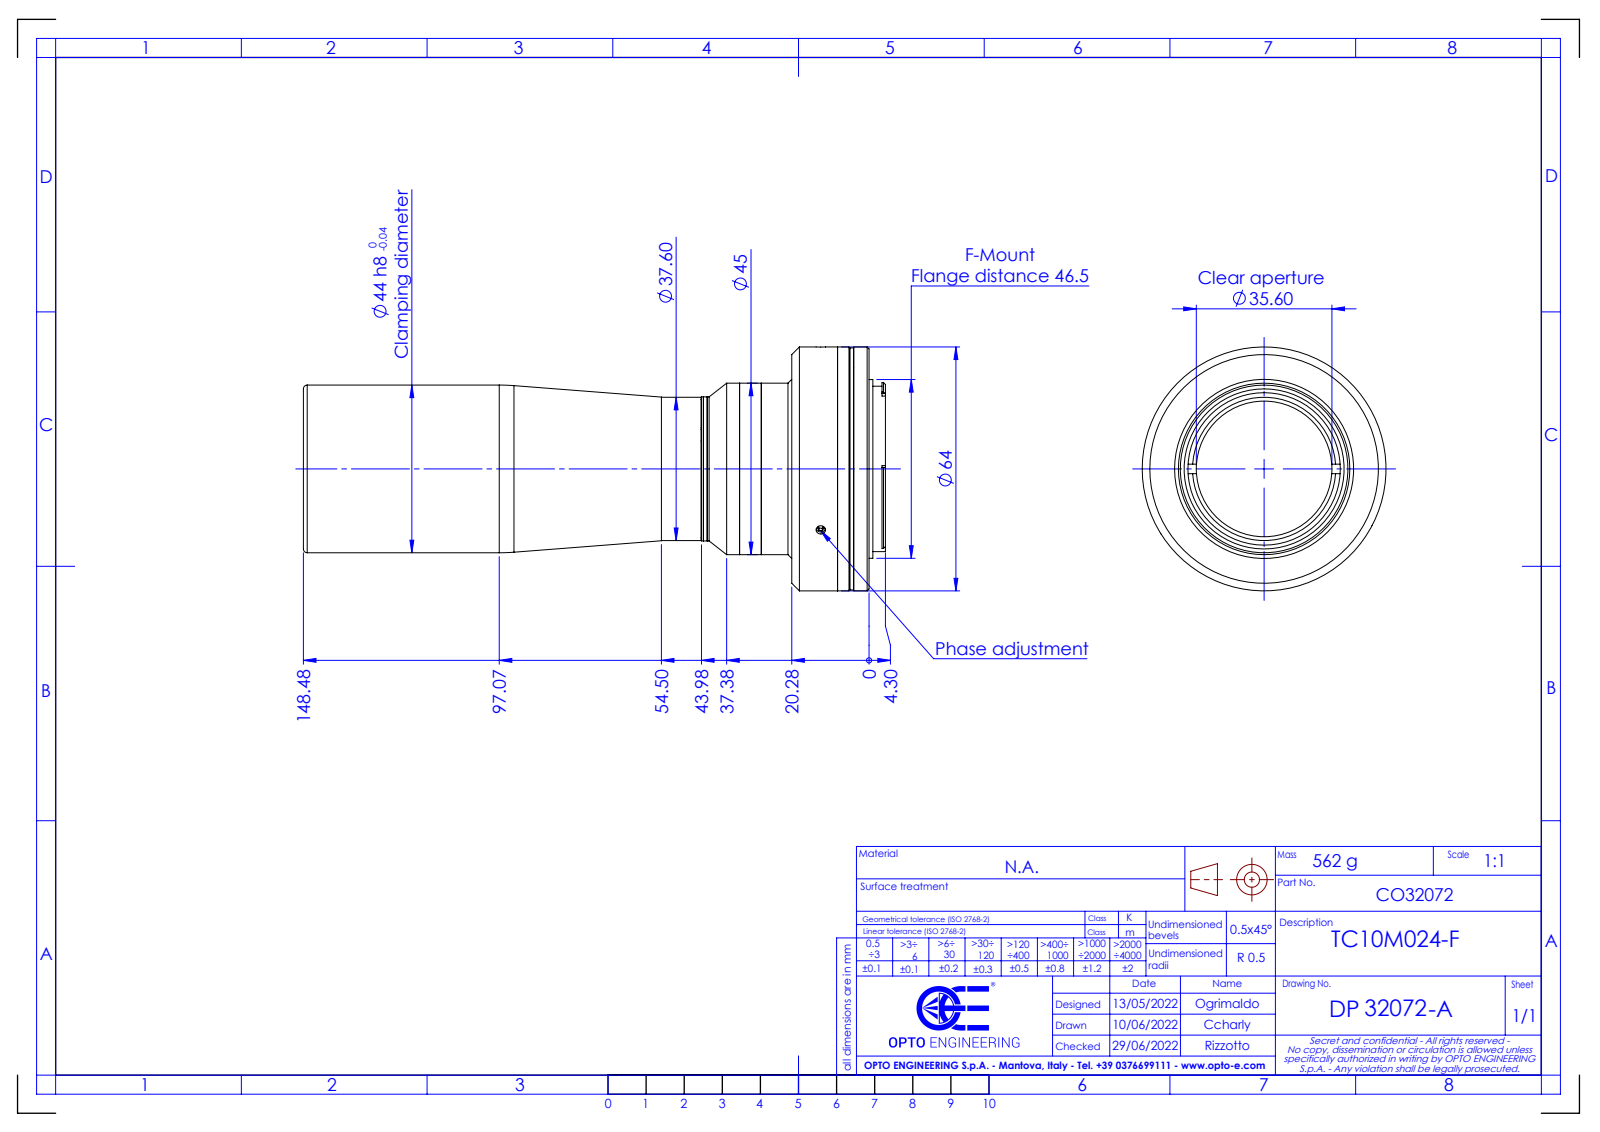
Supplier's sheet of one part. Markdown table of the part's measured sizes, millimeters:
| quantity | value |
| --- | --- |
| part name | DP32072-A_TC10M024-F |
| STEP written by | SolidWorks 2021 (CONFIG_CONTROL_DESIGN) |
| units | millimeters |
| bodies | 0 solids, 145 faces (53 planar, 59 cylindrical, 33 other) |
| overall size | 152.78 × 64 × 64 |
| round holes (diameter × count) | 2.5 × 3, 31.5 × 1, 33 × 1, 35.6 × 1, 40 × 1, 42 × 1 |
| round bosses / shafts (diameter × count) | 64 × 1, 63.5 × 1, 46.9 × 1, 45 × 1, 44 × 1, 43.4 × 1, 37.8 × 1, 37.6 × 1 |
| partial cylindrical surfaces (radius × count) | 0.5 × 6, 1.15 × 2, 22.65 × 1 |
| main face-to-face distances | 12.02, 8.26, 3, 5.26, 15.02, 20.28, 16.28, 4.26, 1.26, 4 |
